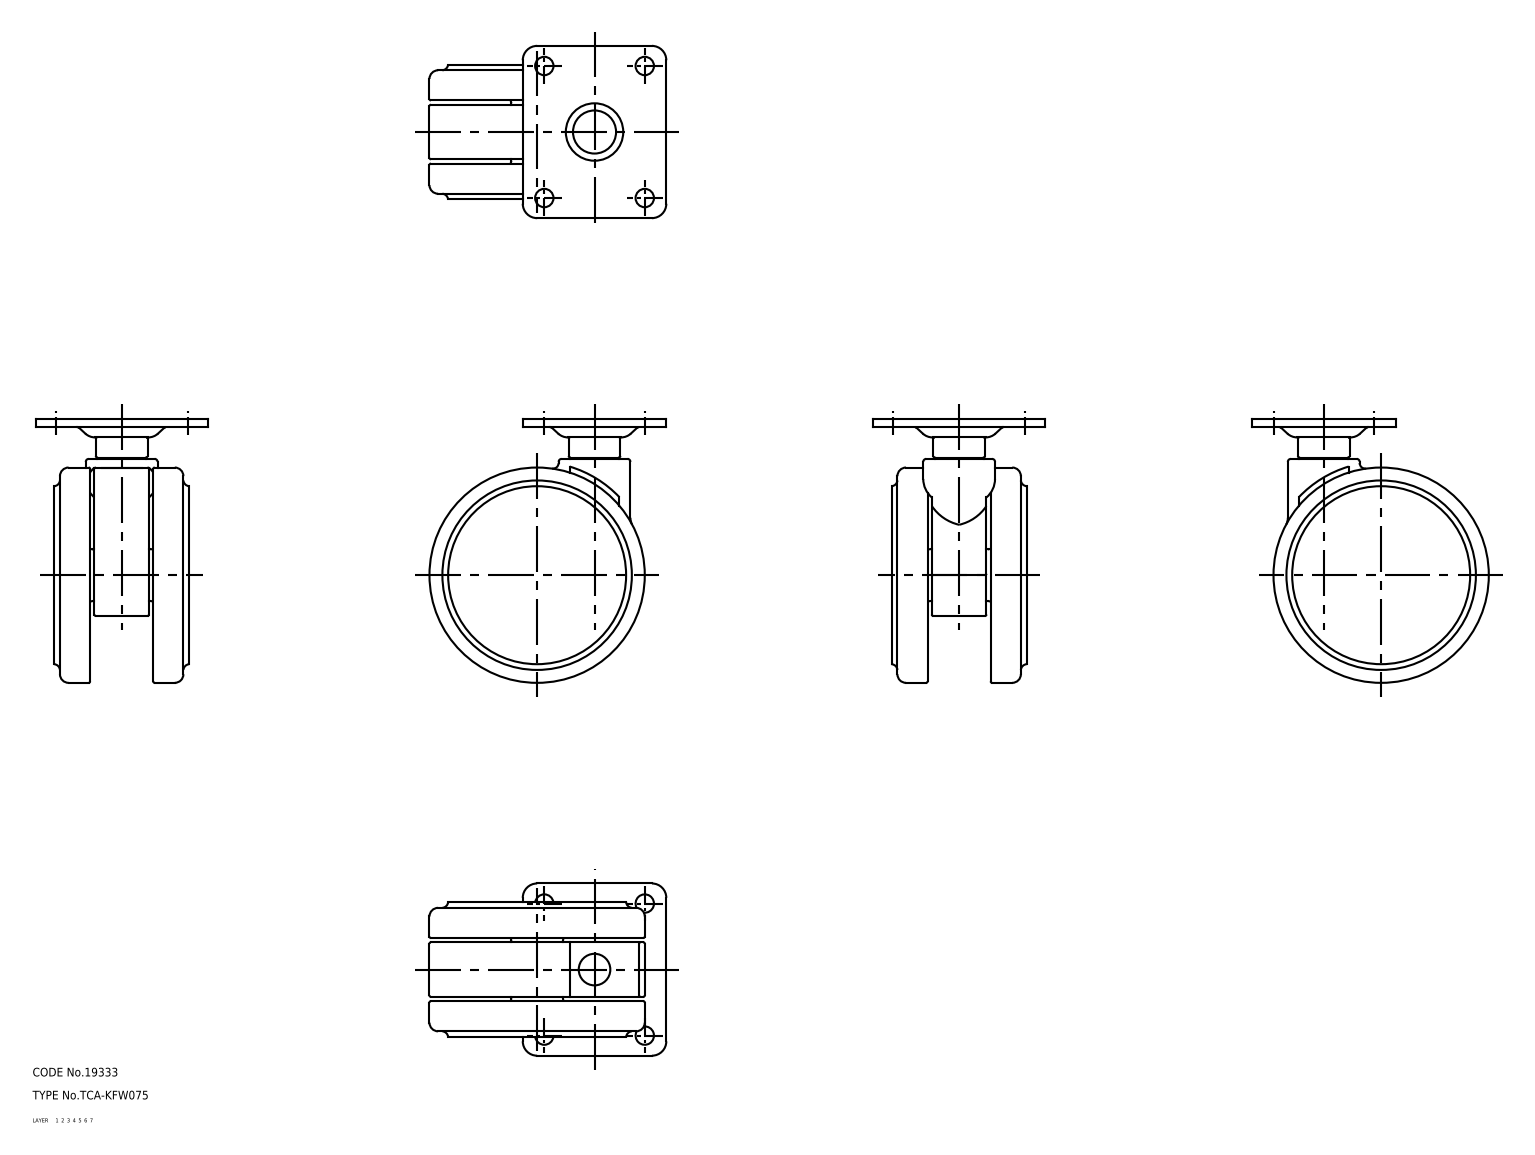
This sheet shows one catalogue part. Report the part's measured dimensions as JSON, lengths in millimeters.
{"part_name": "main shaft; wheel; wheel_mr; mounting plate (+1 more)", "step_written_by": "SolidWorks 2015 (AUTOMOTIVE_DESIGN)", "units": "millimeters", "bodies": {"solids": 5, "faces": 141, "planar": 30, "cylindrical": 56, "other": 55}, "overall_size": [92, 82.5, 60], "volume_mm3": 168223, "surface_area_mm2": 43384, "round_holes": [[6.4, 4], [6, 1], [43, 1]], "round_bosses_or_shafts": [[18, 2], [75, 1], [25, 1], [17, 1], [15, 1]], "partial_cylinders_radius": [[0.5, 11], [5, 4], [1, 1], [2.89, 1], [14.41, 1], [39.5, 1]], "face_to_face_distances": [14, 33, 20.5, 1.5, 12.5, 34.5, 3, 19, 47, 22], "hole_center_spacings": [28.9, 35, 46, 57.8]}
